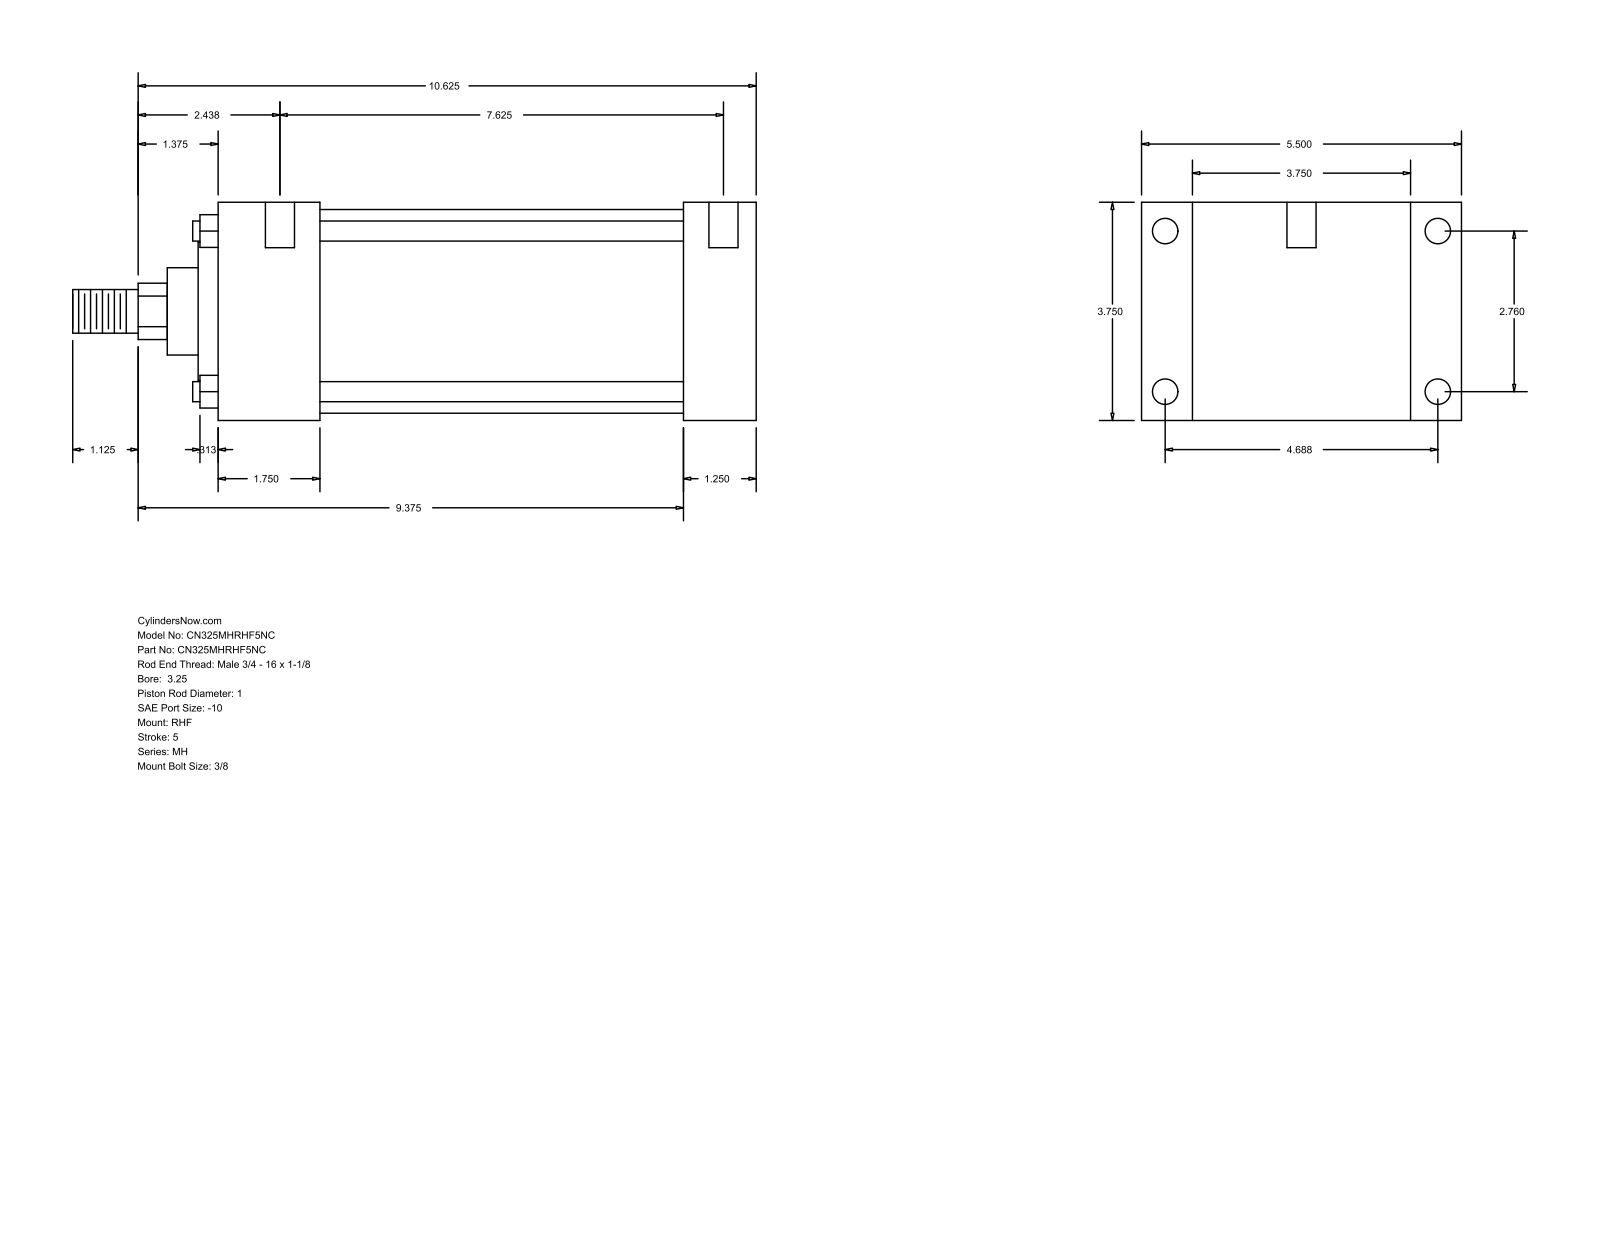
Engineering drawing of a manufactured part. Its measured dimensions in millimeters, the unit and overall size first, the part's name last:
Units: millimetres
Overall size (bounding box): 298.45 × 139.7 × 95.25
Round holes (diameter × count): ⌀5.56 ×4, ⌀11.13 ×4, ⌀12.7 ×2
Round bosses / shafts (diameter × count): ⌀8.76 ×4, ⌀88.9 ×1, ⌀60.33 ×1, ⌀38.1 ×1, ⌀25.4 ×1, ⌀19.05 ×1
Partial cylindrical surfaces — rounded edges, fillets, slot ends (radius × count): R12.29 ×1
Main face-to-face distances: 95.24, 31.76, 22.23, 117.47, 203.2, 234.96, 139.7, 44.46, 158.74, 190.5
Hole centre spacings: 70.1, 119.06, 138.16, 200.02, 1.58, 4.76, 193.68, 195.26
Bodies: 0 solids, 90 faces (61 planar, 29 cylindrical, 0 other)
Part name (STEP PRODUCT): MH_RHF__0325_1
STEP written by: GSSL Pune (CONFIG_CONTROL_DESIGN)
